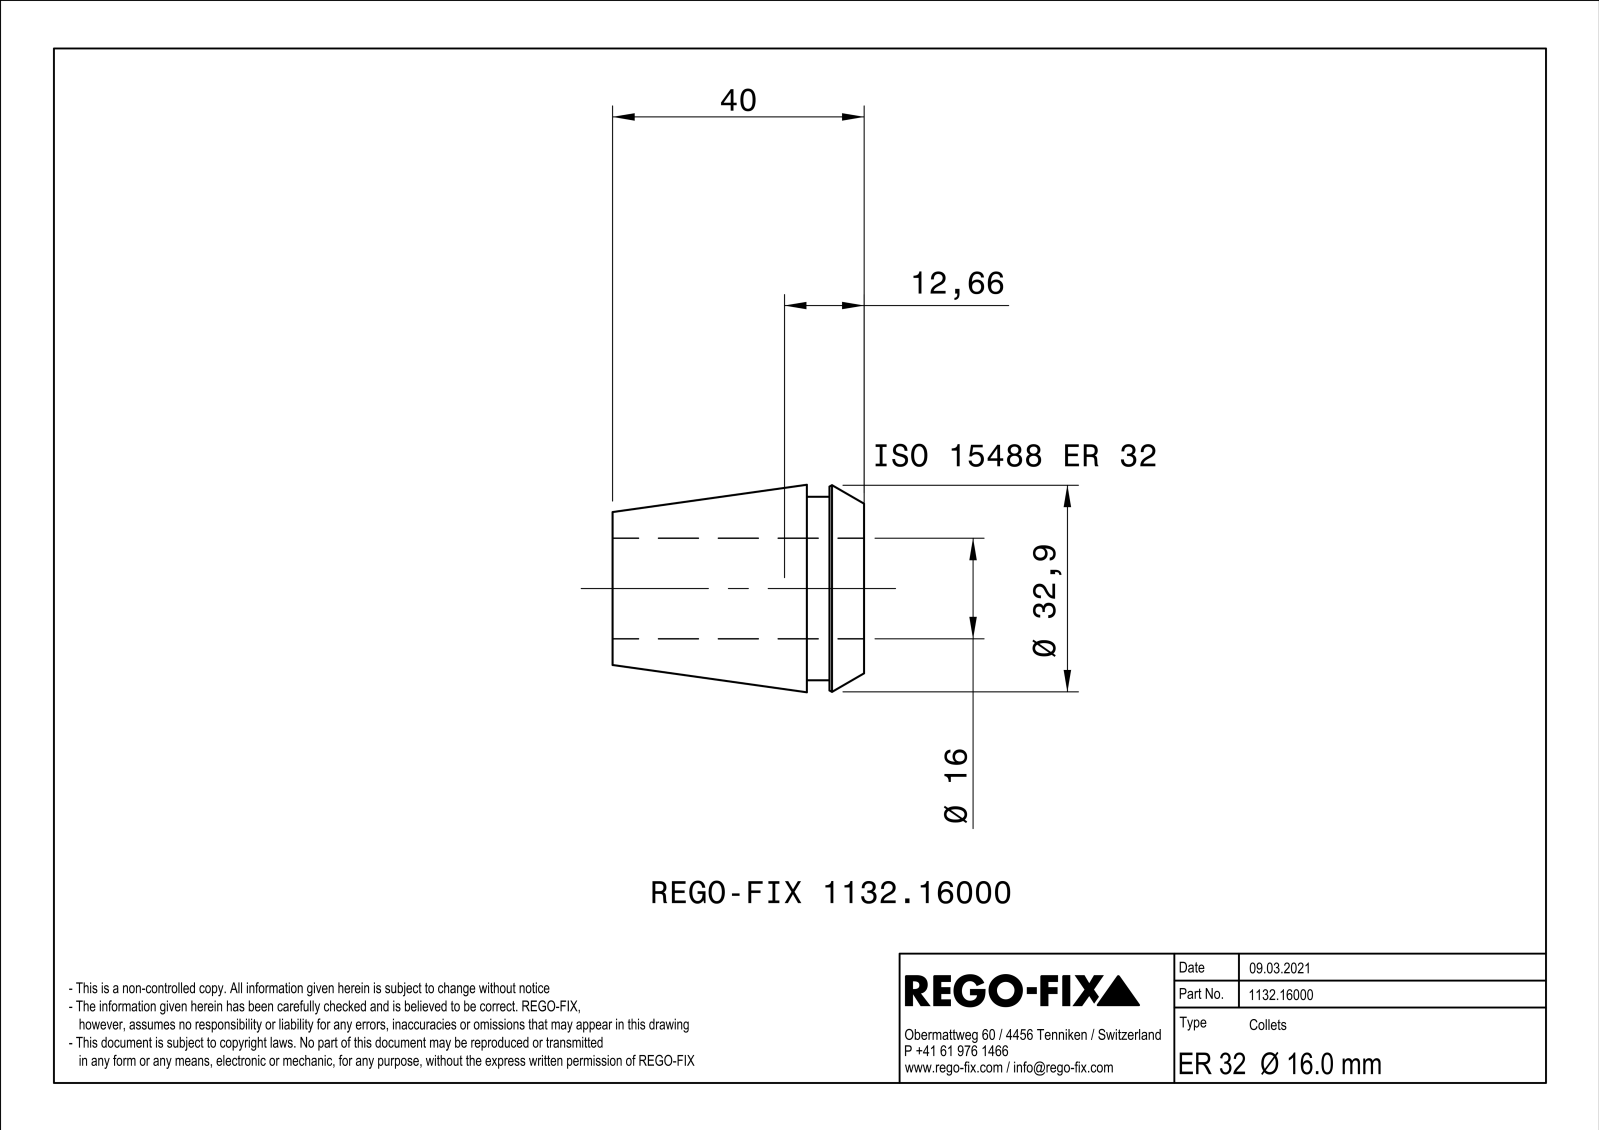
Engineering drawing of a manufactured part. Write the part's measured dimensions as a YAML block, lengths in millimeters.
part_name: "NOCUT"
step_written_by: "SIEMENS PLM Software Solid Edge ST10 (AUTOMOTIVE_DESIGN)"
units: millimeters
bodies: {solids: 1, faces: 209, planar: 88, cylindrical: 41, other: 80}
overall_size: [40, 32.98, 32.98]
volume: 14703
surface_area: 12877
round_holes:
  - {diameter: 16, count: 1}
round_bosses_or_shafts:
  - {diameter: 29.2, count: 1}
partial_cylinders:
  - {radius: 0.4, count: 20}
face_to_face_distances: [1, 40, 9.1, 30.9, 5.5, 3.6, 34.5, 6, 0.5, 3.1]
